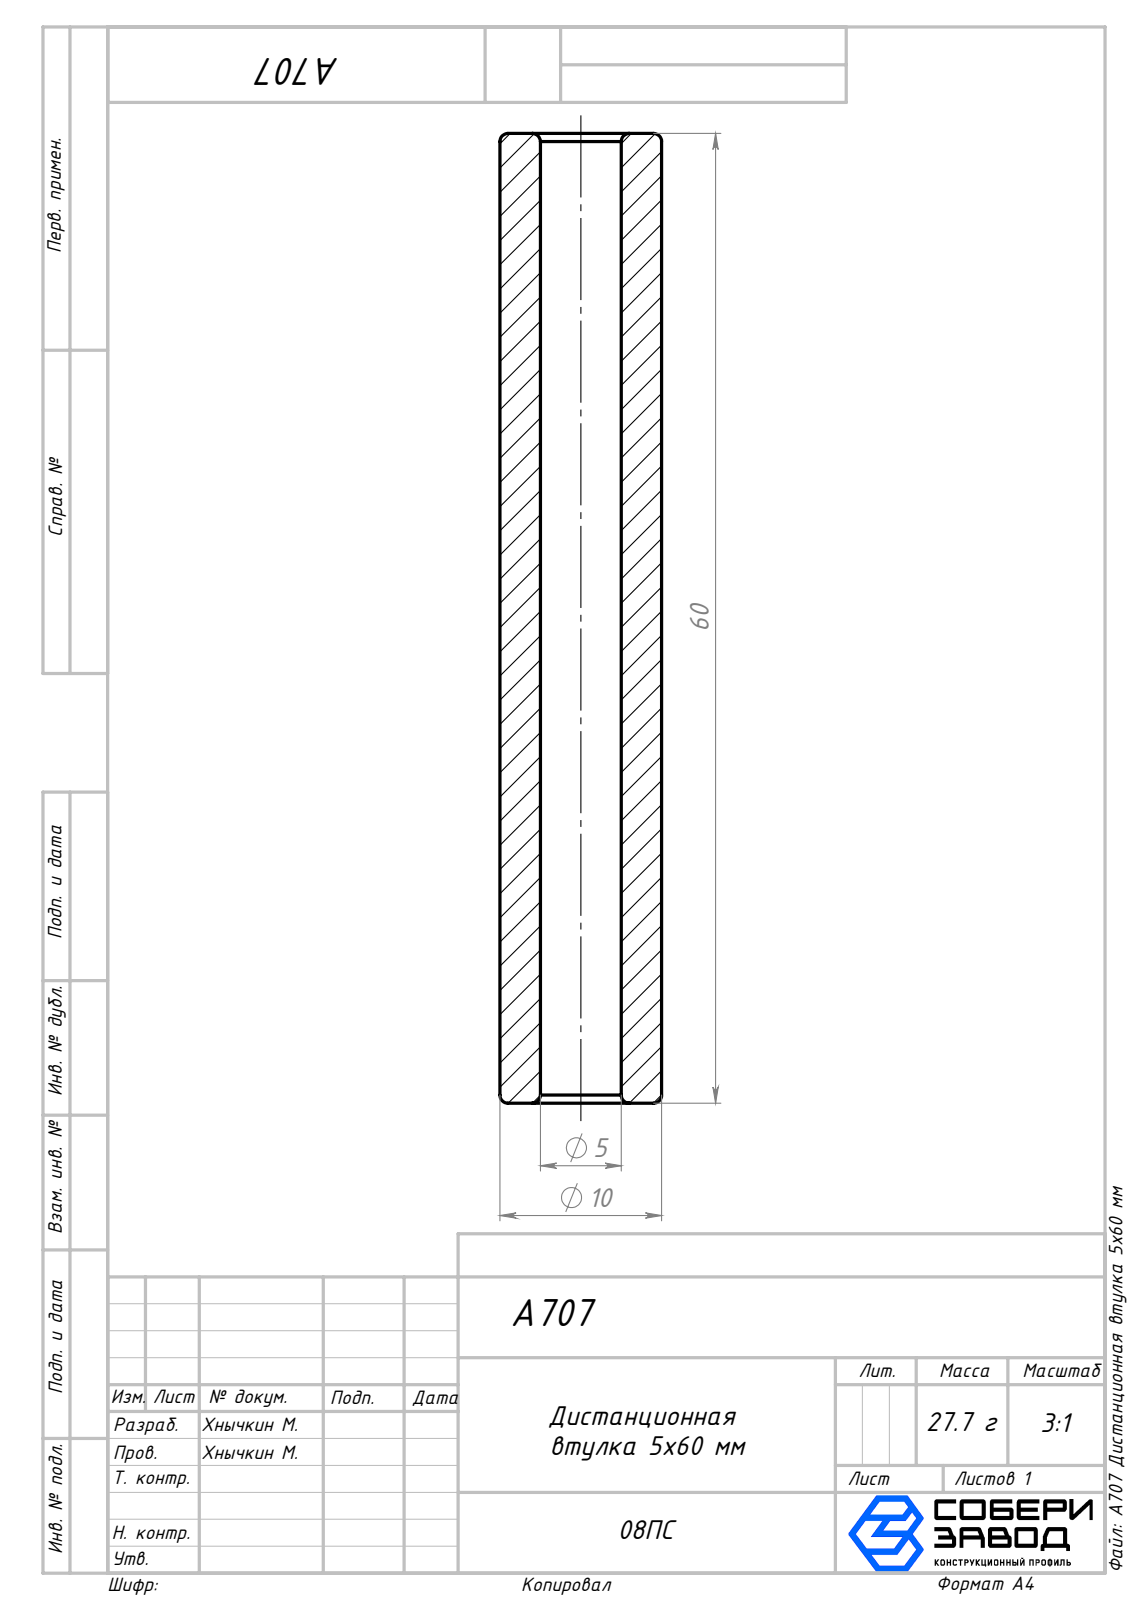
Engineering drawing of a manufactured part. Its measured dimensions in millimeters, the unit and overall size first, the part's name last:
Units: millimetres
Overall size (bounding box): 60 × 10 × 10
Round holes (diameter × count): ⌀5 ×1
Round bosses / shafts (diameter × count): ⌀10 ×1
Main face-to-face distances: 60
Volume: 3 529 mm³ · Surface area: 2 925 mm²
Bodies: 1 solid, 14 faces (2 planar, 4 cylindrical, 8 other)
Part name (STEP PRODUCT): A707 Дистанционная втулка 5x60 мм
STEP written by: SolidWorks 2026 (AUTOMOTIVE_DESIGN)
